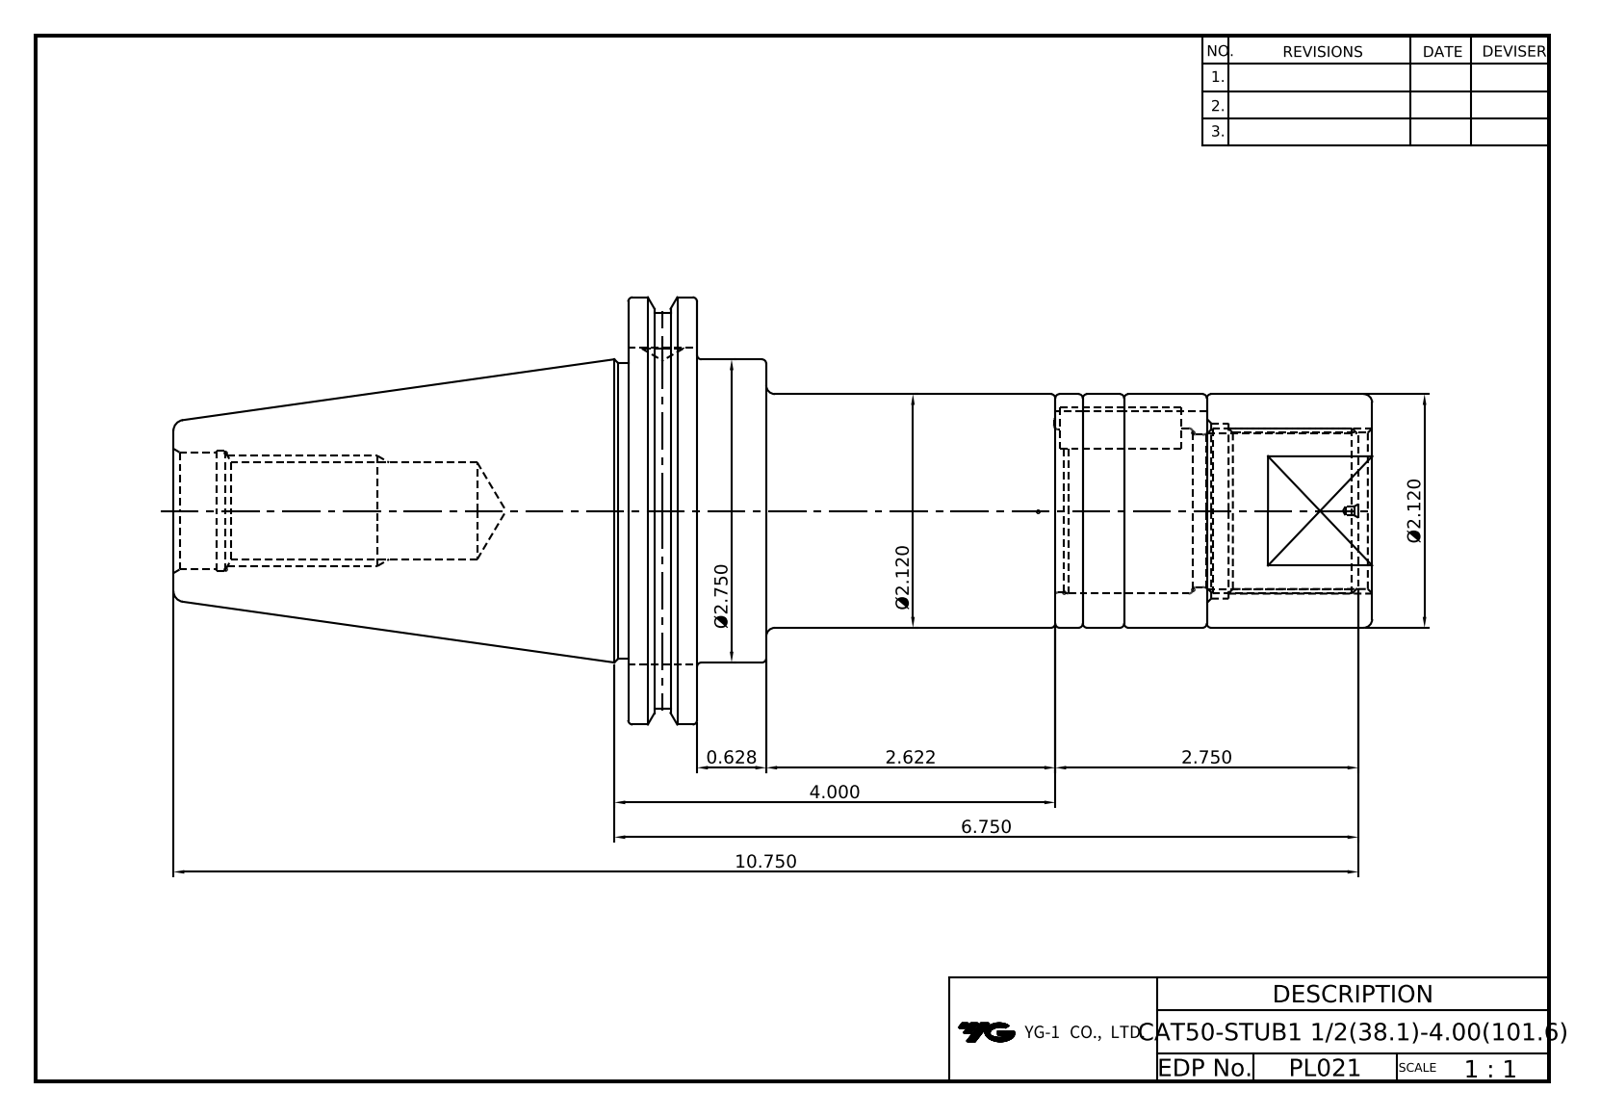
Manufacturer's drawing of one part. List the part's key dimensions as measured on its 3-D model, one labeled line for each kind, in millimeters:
Part name (STEP PRODUCT): LO-CAT50-STUB38.1-101.6; 9.525x9.525x28; COLLAR_STUB38.1(6.35T); COLLAR_STUB38.1(9.525T) (+2 more)
STEP written by: Autodesk Inventor 2025 (AP242_MANAGED_MODEL_BASED_3D_ENGINEERING_MIM_LF)
Units: millimetres
Bodies: 6 solids, 113 faces (59 planar, 28 cylindrical, 26 other)
Overall size (bounding box): 274.88 × 98.42 × 94.69
Volume: 711 065 mm³ · Surface area: 95 102 mm²
Round holes (diameter × count): ⌀9.53 ×1, ⌀21.97 ×1, ⌀26.2 ×1, ⌀35.81 ×1, ⌀38.1 ×1, ⌀40.4 ×1
Round bosses / shafts (diameter × count): ⌀98.42 ×1, ⌀91.29 ×1, ⌀69.85 ×1, ⌀69.25 ×1, ⌀53.85 ×1, ⌀35 ×1
Partial cylindrical surfaces — rounded edges, fillets, slot ends (radius × count): R4.76 ×2, R4.76 ×2
Main face-to-face distances: 15.88, 9.52, 98.43, 82.55, 103.43, 112.95, 87.55, 97.07, 5, 14.52
